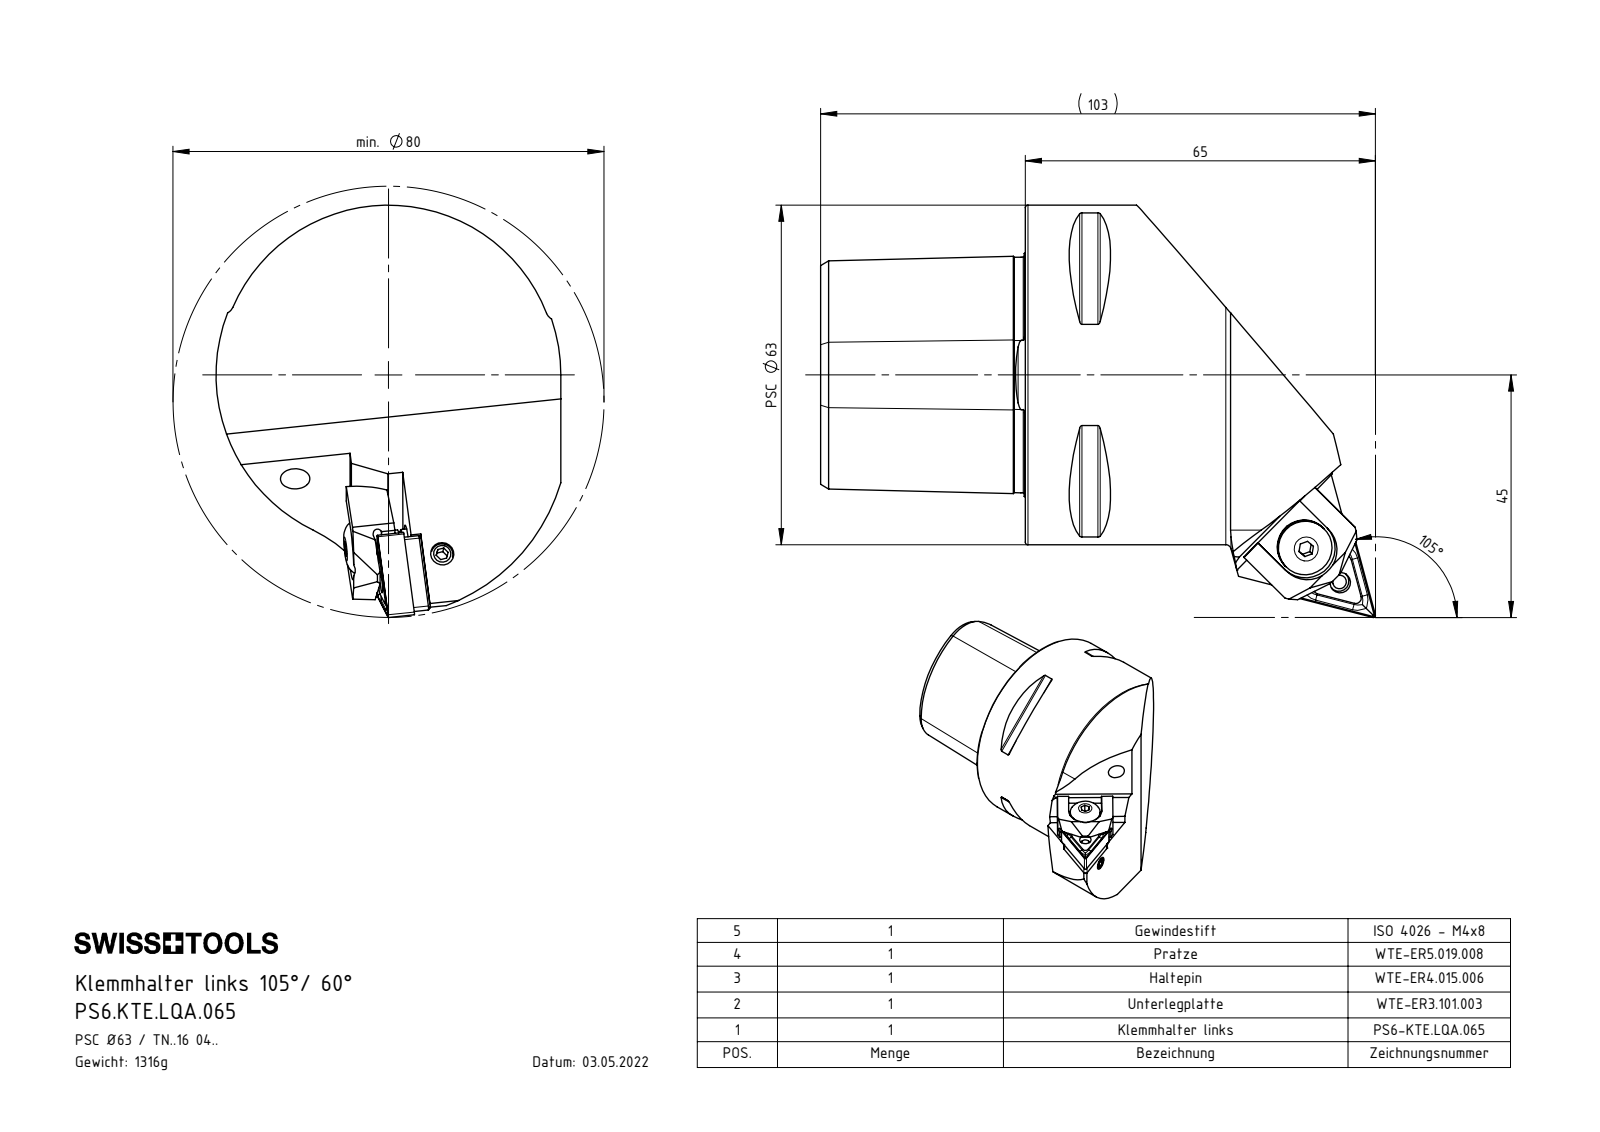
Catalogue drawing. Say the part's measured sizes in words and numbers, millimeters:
The part is named "PS6.KTE.LQA.065; WTE-ER4.015.006_A; WTE-ER3.101.003_A; KVT_MB_600_060 (+6 more)". Its 3-D file was written by "SolidWorks 2017 (AUTOMOTIVE_DESIGN)". It is 12 solids with 391 faces: 107 planar, 114 cylindrical and 170 other. Overall it measures 103 by 76.5 by 64 millimeters. Its volume is 170 044 cubic millimeters and its surface area 32 535 square millimeters. Round holes: 6 of diameter 5, 2 of diameter 6, 1 of diameter 3.3, 1 of diameter 3.81, 1 of diameter 4, 1 of diameter 4.2, 1 of diameter 5.05, 1 of diameter 5.3, 1 of diameter 6.55, 1 of diameter 6.8, 1 of diameter 8.1, 1 of diameter 18. Round bosses or shafts: 3 of diameter 6, 2 of diameter 5, 1 of diameter 63, 1 of diameter 10, 1 of diameter 4.5, 1 of diameter 4, 1 of diameter 3.7, 1 of diameter 3.5. Partial cylindrical surfaces (rounded edges, fillets, slot ends): 8 of radius 0.5, 3 of radius 0.4, 3 of radius 0.6, 3 of radius 1, 2 of radius 2.7, 1 of radius 0.8, 1 of radius 0.84, 1 of radius 5.5. The main face-to-face distances are 38, 24.88, 11, 27, 3, 1.39, 55.8, 7.5, 6.11, 4.5. The hole center spacings are 9.76, 9.77, 27.5.
